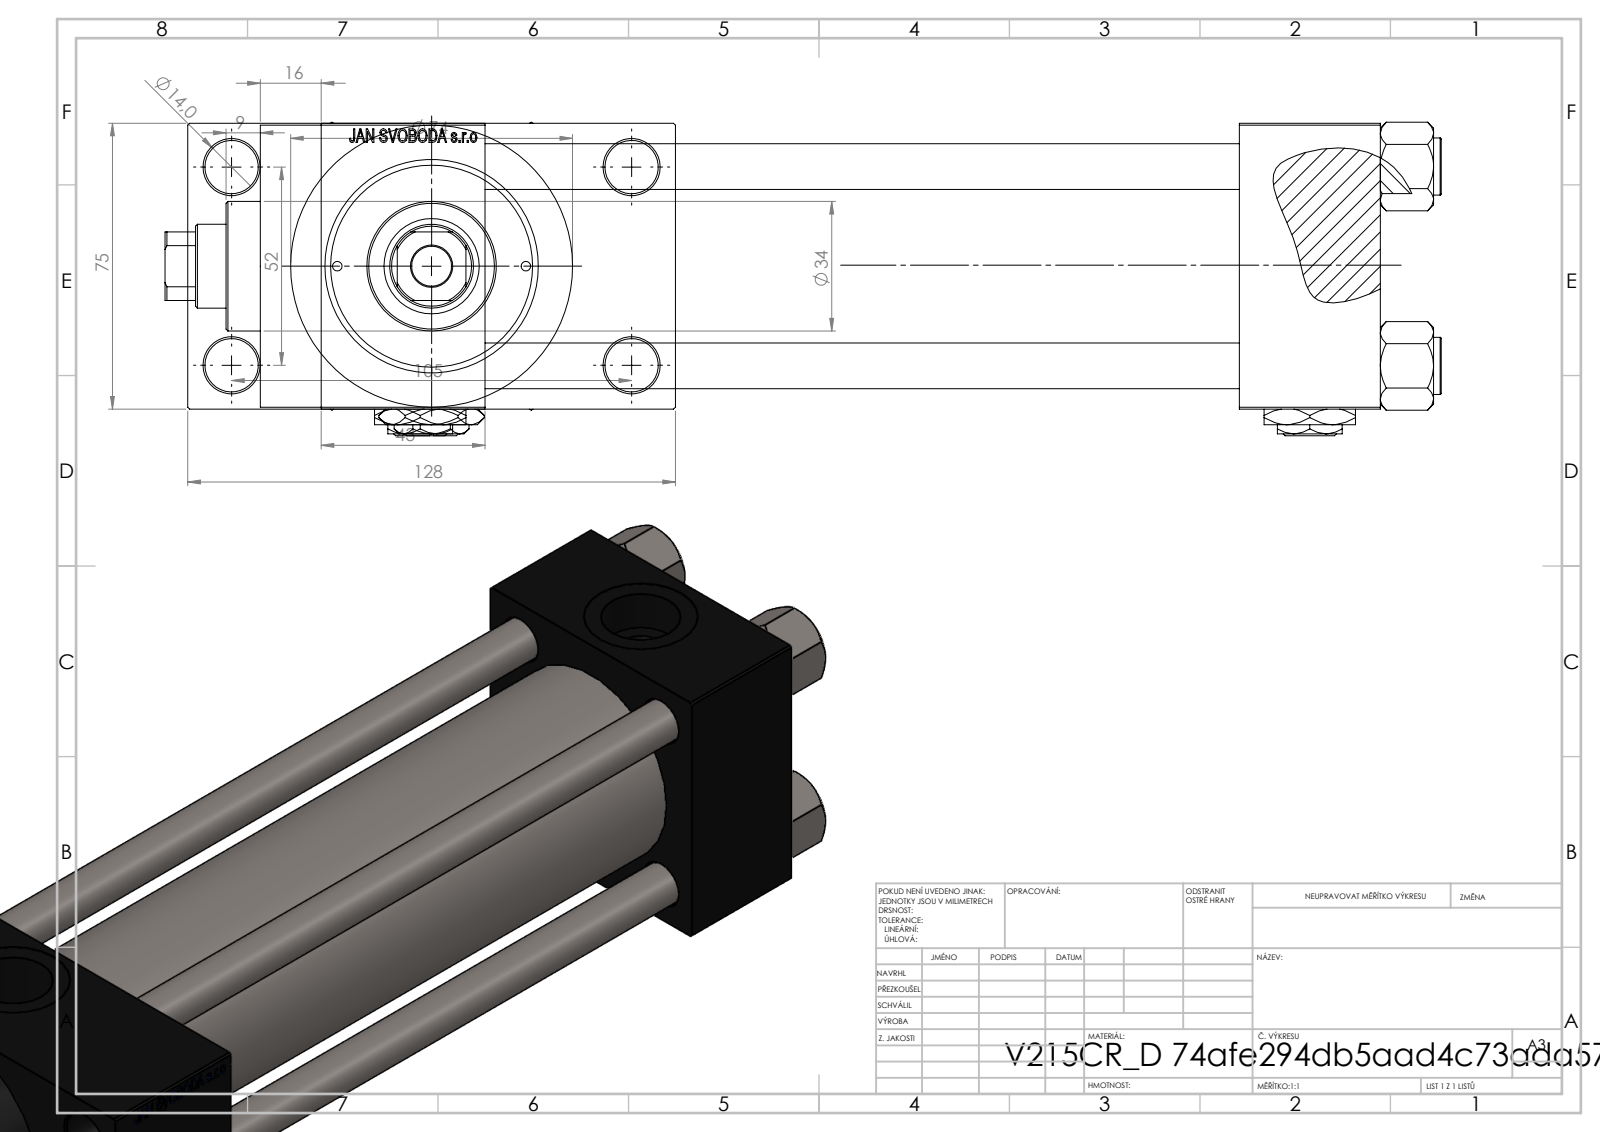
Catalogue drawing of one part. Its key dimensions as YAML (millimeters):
part_name: "V215CR_D_Body; V215_VC_A; NUT_M5_D; Zatka_pro_OIL_PORT (+2 more)"
step_written_by: "SolidWorks 2019 (CONFIG_CONTROL_DESIGN)"
units: millimeters
bodies: {solids: 13, faces: 1213, planar: 547, cylindrical: 104, other: 562}
overall_size: [335, 128, 82.27]
volume: 988422
surface_area: 246527
round_holes:
  - {diameter: 12, count: 4}
  - {diameter: 14, count: 4}
  - {diameter: 2.5, count: 2}
  - {diameter: 7, count: 2}
  - {diameter: 20.96, count: 2}
  - {diameter: 30, count: 2}
  - {diameter: 10.5, count: 1}
  - {diameter: 22, count: 1}
  - {diameter: 25, count: 1}
  - {diameter: 41, count: 1}
  - {diameter: 50, count: 1}
  - {diameter: 53, count: 1}
round_bosses_or_shafts:
  - {diameter: 15, count: 4}
  - {diameter: 74, count: 1}
  - {diameter: 56, count: 1}
  - {diameter: 34, count: 1}
partial_cylinders:
  - {radius: 10.5, count: 1}
face_to_face_distances: [75, 198, 37, 235, 26.5, 101.5, 278, 241, 43, 16]
hole_center_spacings: [26.19, 26.35, 36.98, 38.03, 52.3, 57.22, 58.43, 58.59]
